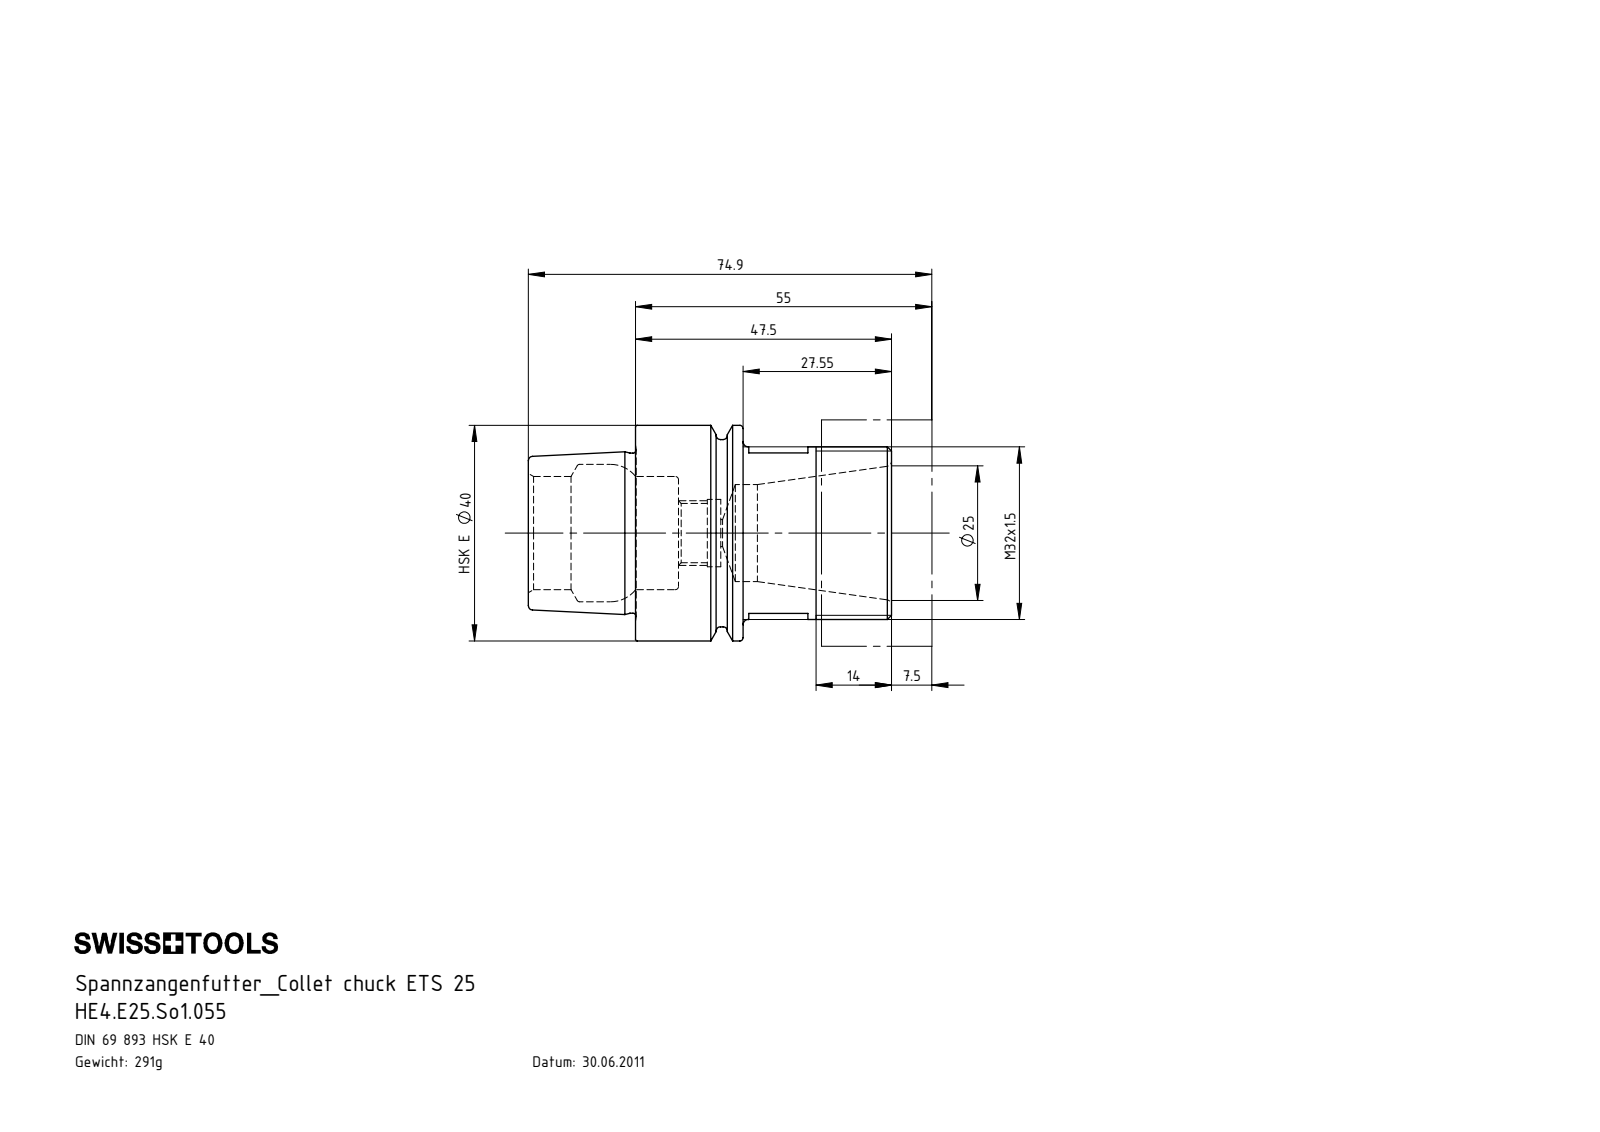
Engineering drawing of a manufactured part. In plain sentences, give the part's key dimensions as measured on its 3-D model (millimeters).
The part is named "HE4-E25.So1.055_A_Fertigbearbeitung; HE4-E25.So1.055". Its 3-D file was written by "SolidWorks 2015 (AUTOMOTIVE_DESIGN)". It is 1 solid with 85 faces: 15 planar, 24 cylindrical and 46 other. Overall it measures 67.4 by 40 by 40 millimeters. Its volume is 37 115 cubic millimeters and its surface area 13 799 square millimeters. Round holes: 1 of diameter 5, 1 of diameter 11, 1 of diameter 12.5, 1 of diameter 18, 1 of diameter 21, 1 of diameter 25.5. Round bosses or shafts: 1 of diameter 40, 1 of diameter 34.75, 1 of diameter 32, 1 of diameter 29.71. The main face-to-face distances are 19.95, 7.95, 12, 19.9, 27.85, 39.85, 67.4, 47.5, 39.55, 27.55.
